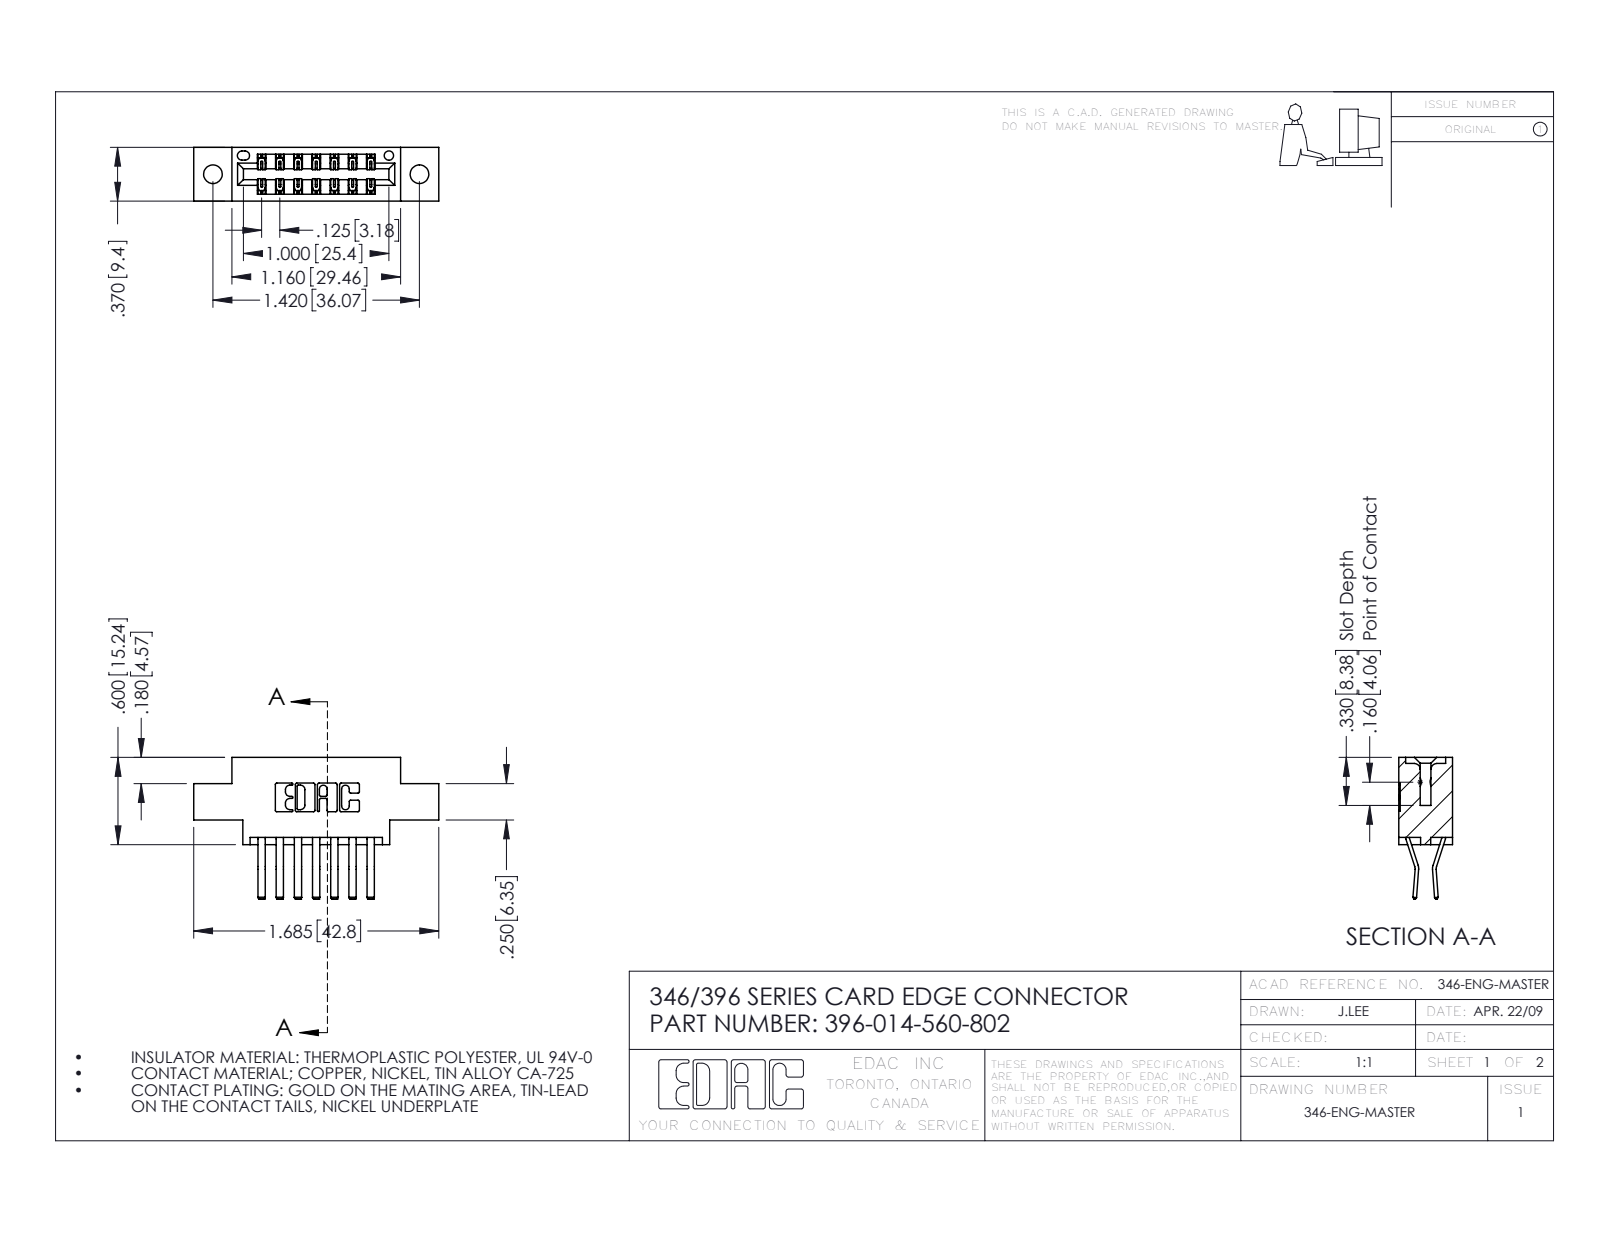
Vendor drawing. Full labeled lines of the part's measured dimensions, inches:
Part name (STEP PRODUCT): 346 Part_0.170 Offset - 0.128 Dia; 396-014-560-802; 345-292-001_560 Tail
STEP written by: SolidWorks 2016 (CONFIG_CONTROL_DESIGN)
Units: inches
Bodies: 15 solids, 882 faces (570 planar, 312 cylindrical, 0 other)
Overall size (bounding box): 1.685 × 0.975 × 0.37
Volume: 0.232 in³ · Surface area: 7.488 in²
Round holes (diameter × count): ⌀0.128 ×2, ⌀0.064 ×1
Partial cylindrical surfaces — rounded edges, fillets, slot ends (radius × count): R0.01 ×22, R0.006 ×21, R0.007 ×6, R0.031 ×6, R0.026 ×3, R0.01 ×2, R0.014 ×2, R0.022 ×2
Main face-to-face distances: 0.25, 0.37, 0.048, 0.322, 0.025, 0.148, 0.222, 0.1, 0.174, 0.072
Hole centre spacings: 0.246, 1.217, 1.42
